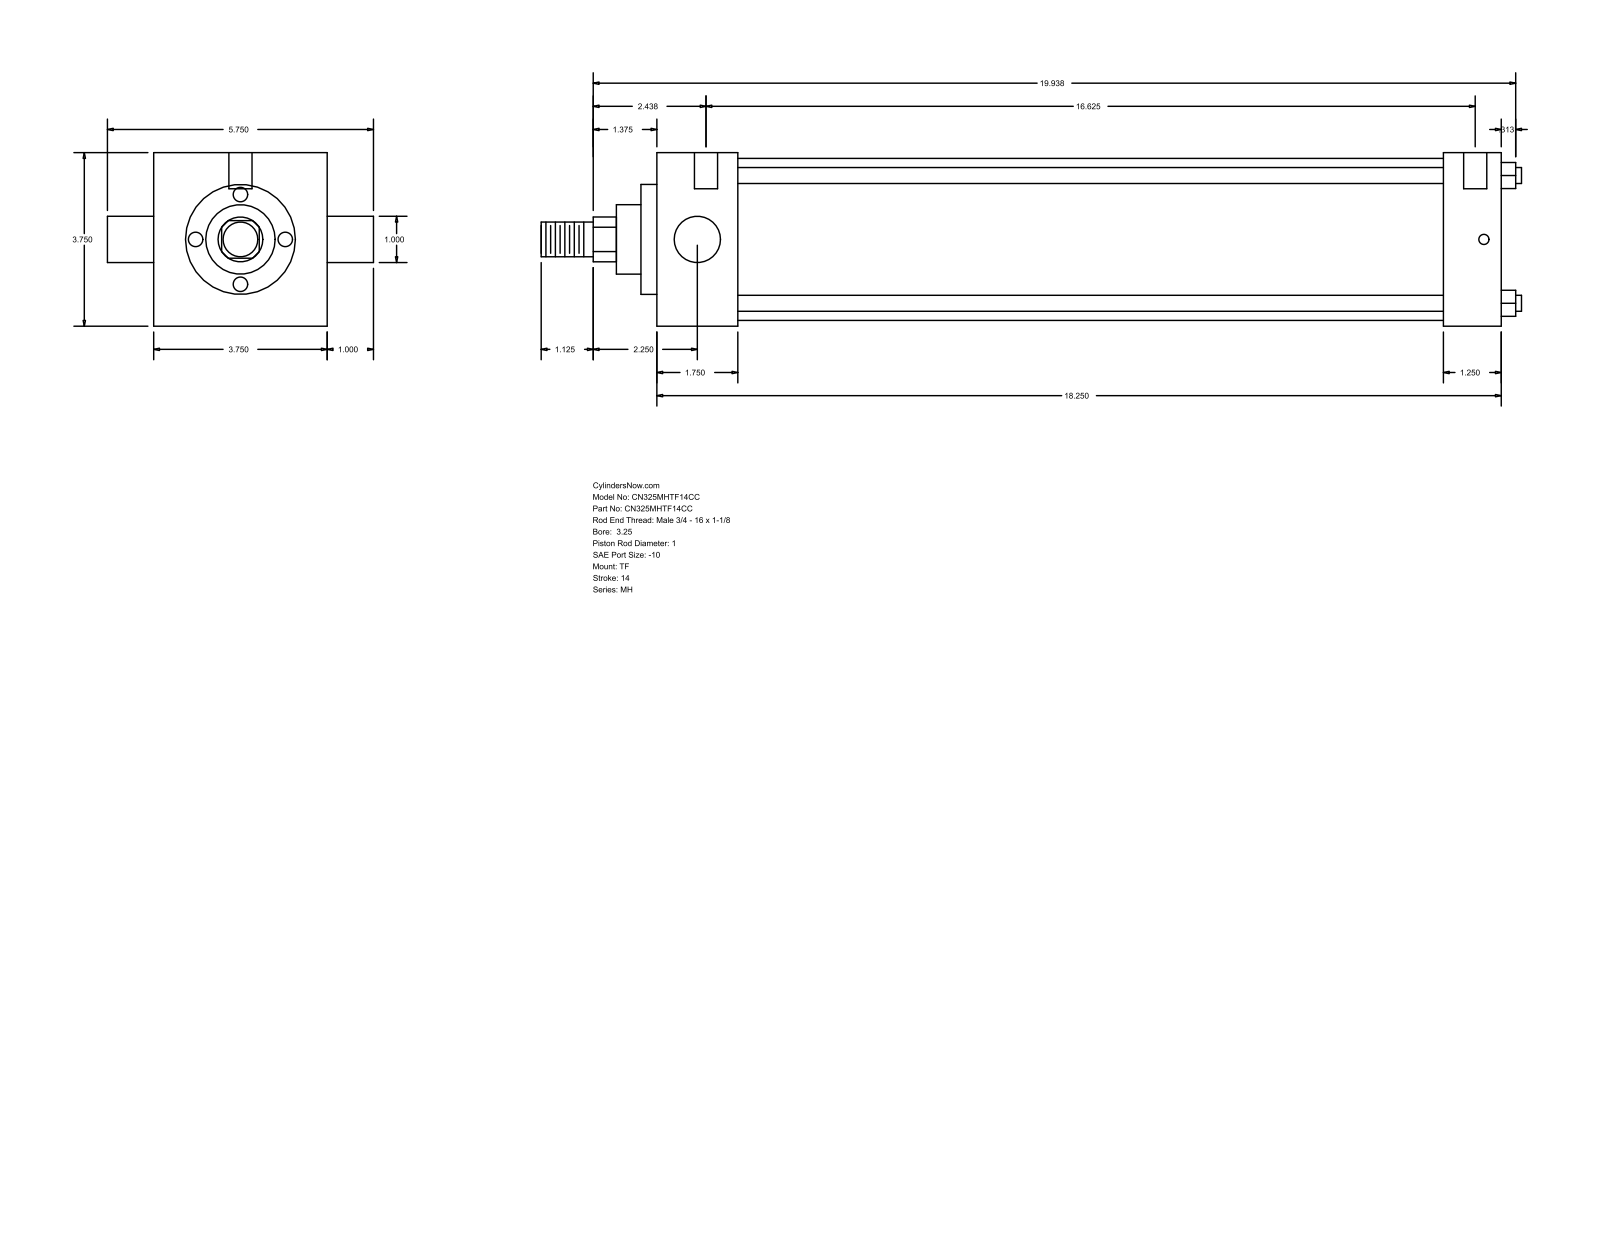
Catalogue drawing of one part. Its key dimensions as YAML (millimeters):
part_name: "MH_TF__0325_1"
step_written_by: "GSSL Pune (CONFIG_CONTROL_DESIGN)"
units: millimeters
bodies: {solids: 0, faces: 86, planar: 61, cylindrical: 25, other: 0}
overall_size: [538.16, 146.05, 95.25]
round_holes:
  - {diameter: 5.56, count: 3}
  - {diameter: 12.7, count: 2}
round_bosses_or_shafts:
  - {diameter: 8.76, count: 4}
  - {diameter: 25.4, count: 2}
  - {diameter: 88.9, count: 1}
  - {diameter: 60.33, count: 1}
  - {diameter: 38.1, count: 1}
  - {diameter: 19.05, count: 1}
partial_cylinders:
  - {radius: 12.29, count: 1}
face_to_face_distances: [95.24, 463.56, 44.46, 431.81, 387.35, 419.1, 31.75, 8.73, 53.19, 440.54]
hole_center_spacings: [1.58, 4.76, 422.28, 423.86, 427.04, 428.62]
